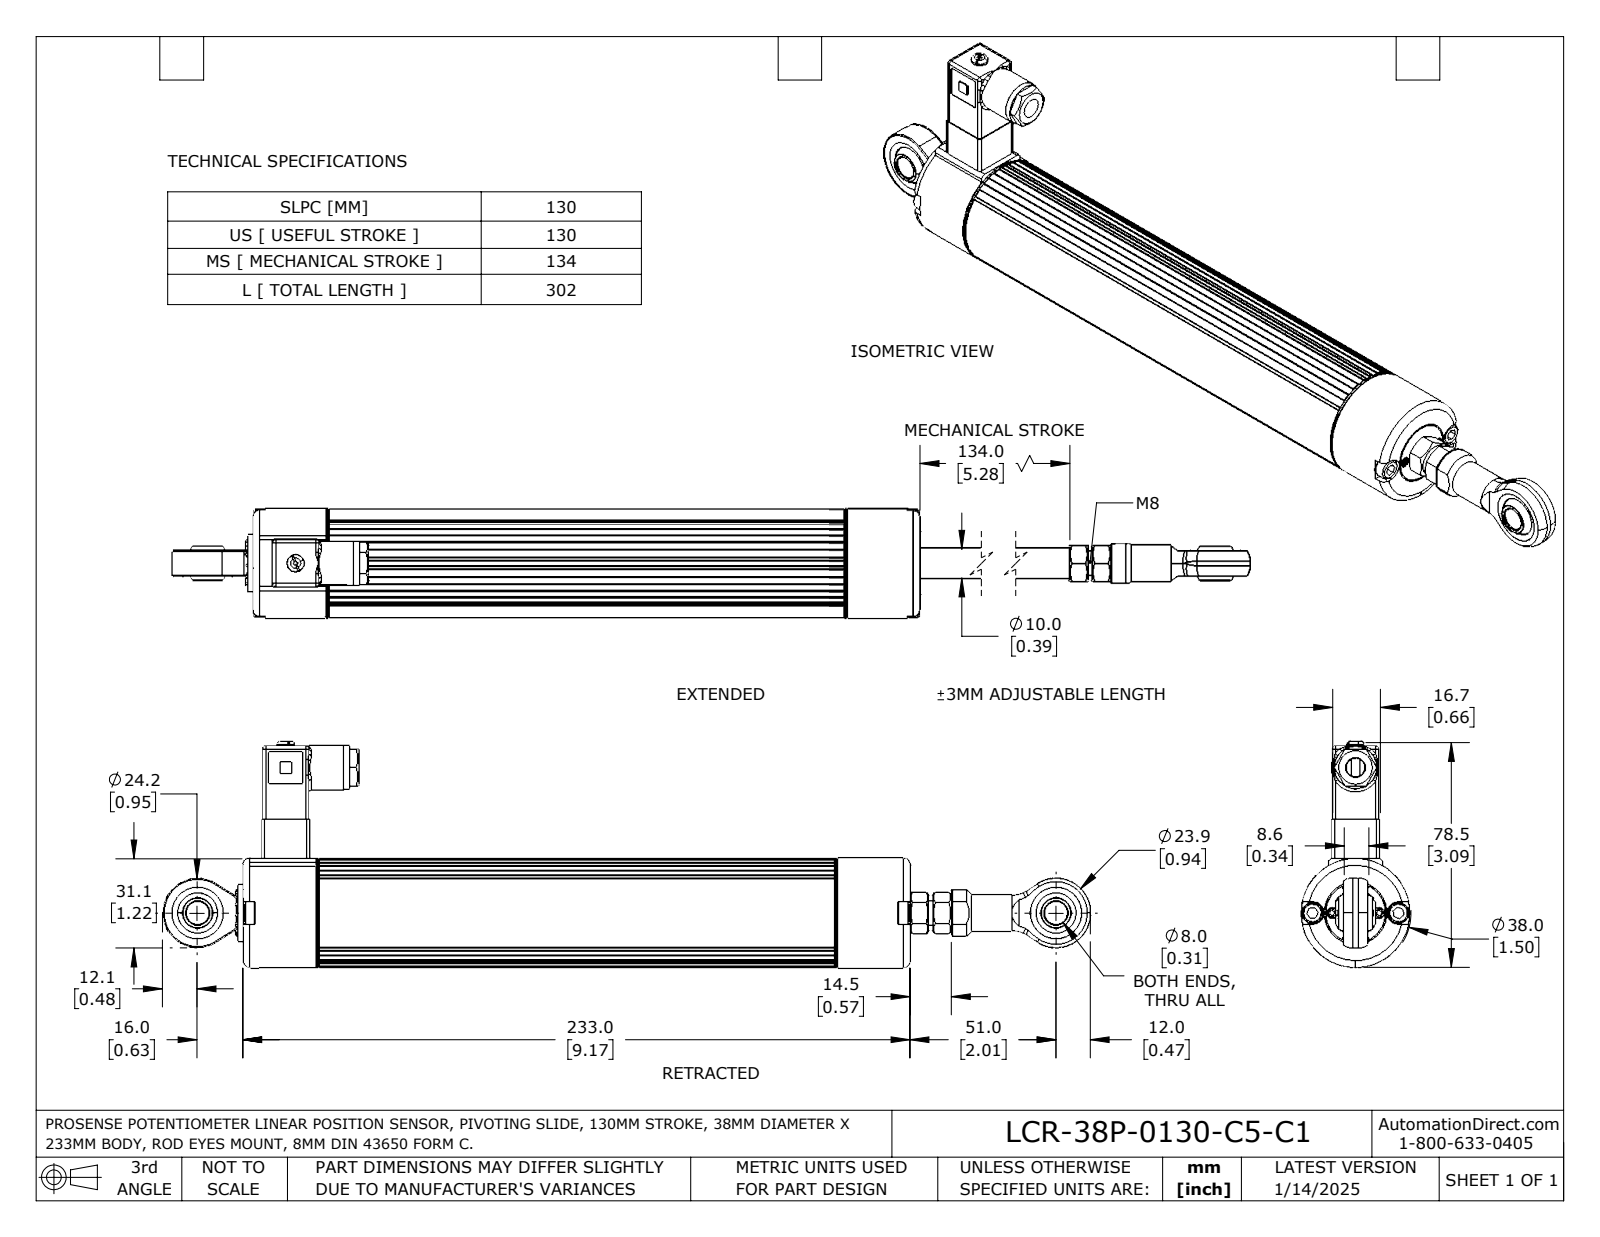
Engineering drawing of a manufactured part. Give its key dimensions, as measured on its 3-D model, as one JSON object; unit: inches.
{"part_name": "LCR-38P-0130-C5-C1", "step_written_by": "SolidWorks 2023 (AUTOMOTIVE_DESIGN)", "units": "inches", "bodies": {"solids": 11, "faces": 657, "planar": 295, "cylindrical": 210, "other": 152}, "overall_size": [12.758, 3.093, 1.488], "volume_in3": 16.99, "surface_area_in2": 92.55, "round_holes": [[0.102, 6], [0.091, 4], [0.315, 3], [0.551, 3], [0.094, 2], [0.1, 2], [0.111, 2], [0.134, 2], [0.152, 2], [0.165, 2], [0.079, 1], [0.118, 1]], "round_bosses_or_shafts": [[0.063, 6], [0.283, 4], [0.15, 4], [0.48, 2], [0.079, 2], [1.488, 1], [0.823, 1], [0.768, 1]], "partial_cylinders_radius": [[0.008, 32], [0.039, 20], [0.02, 12], [0.016, 6], [0.012, 2], [0.059, 2], [0.083, 2], [0.098, 2]], "face_to_face_distances": [7.087, 1.043, 8.13, 0.031, 0.045, 0.612, 0.598, 0.014, 0.644, 0.138], "hole_center_spacings": [0.632, 0.075, 0.634, 0.264, 0.268, 0.285, 0.323, 0.394]}
